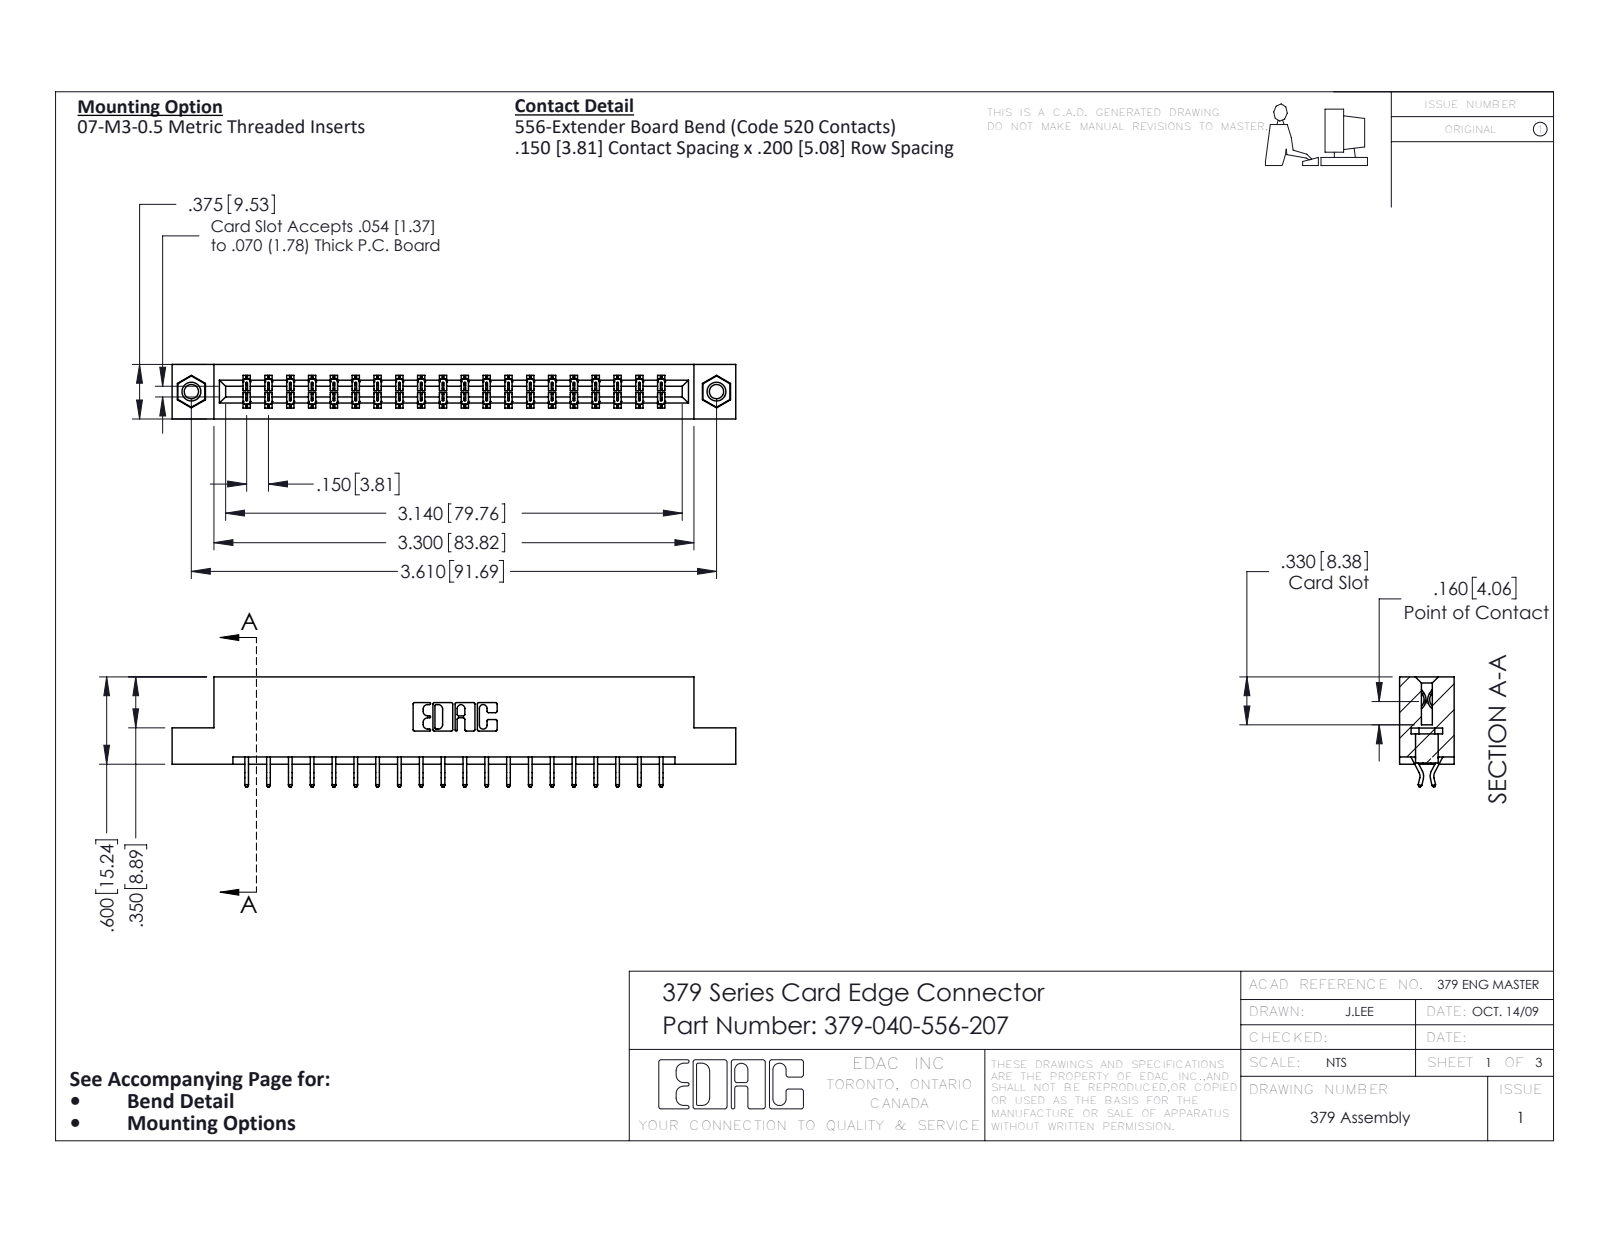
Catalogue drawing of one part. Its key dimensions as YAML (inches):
part_name: "345-250-001_345-250-005-103; 345-292-001_556 Tail; 379-040-556-207; 379 Part_Flush - .156 Dia - TI"
step_written_by: "SolidWorks 2016 (CONFIG_CONTROL_DESIGN)"
units: inches
bodies: {solids: 43, faces: 2494, planar: 1702, cylindrical: 776, other: 16}
overall_size: [3.875, 0.757, 0.375]
volume: 0.622
surface_area: 17.43
round_holes:
  - {diameter: 0.098, count: 2}
  - {diameter: 0.125, count: 2}
  - {diameter: 0.156, count: 2}
round_bosses_or_shafts:
  - {diameter: 0.155, count: 2}
partial_cylinders:
  - {radius: 0.006, count: 60}
  - {radius: 0.01, count: 22}
  - {radius: 0.007, count: 6}
  - {radius: 0.031, count: 6}
  - {radius: 0.026, count: 3}
  - {radius: 0.01, count: 2}
  - {radius: 0.014, count: 2}
  - {radius: 0.022, count: 2}
face_to_face_distances: [0.3, 0.075, 0.375, 0.6, 0.225, 0.15, 0.45, 0.2, 0.076, 0.15]
hole_center_spacings: [3.61]
